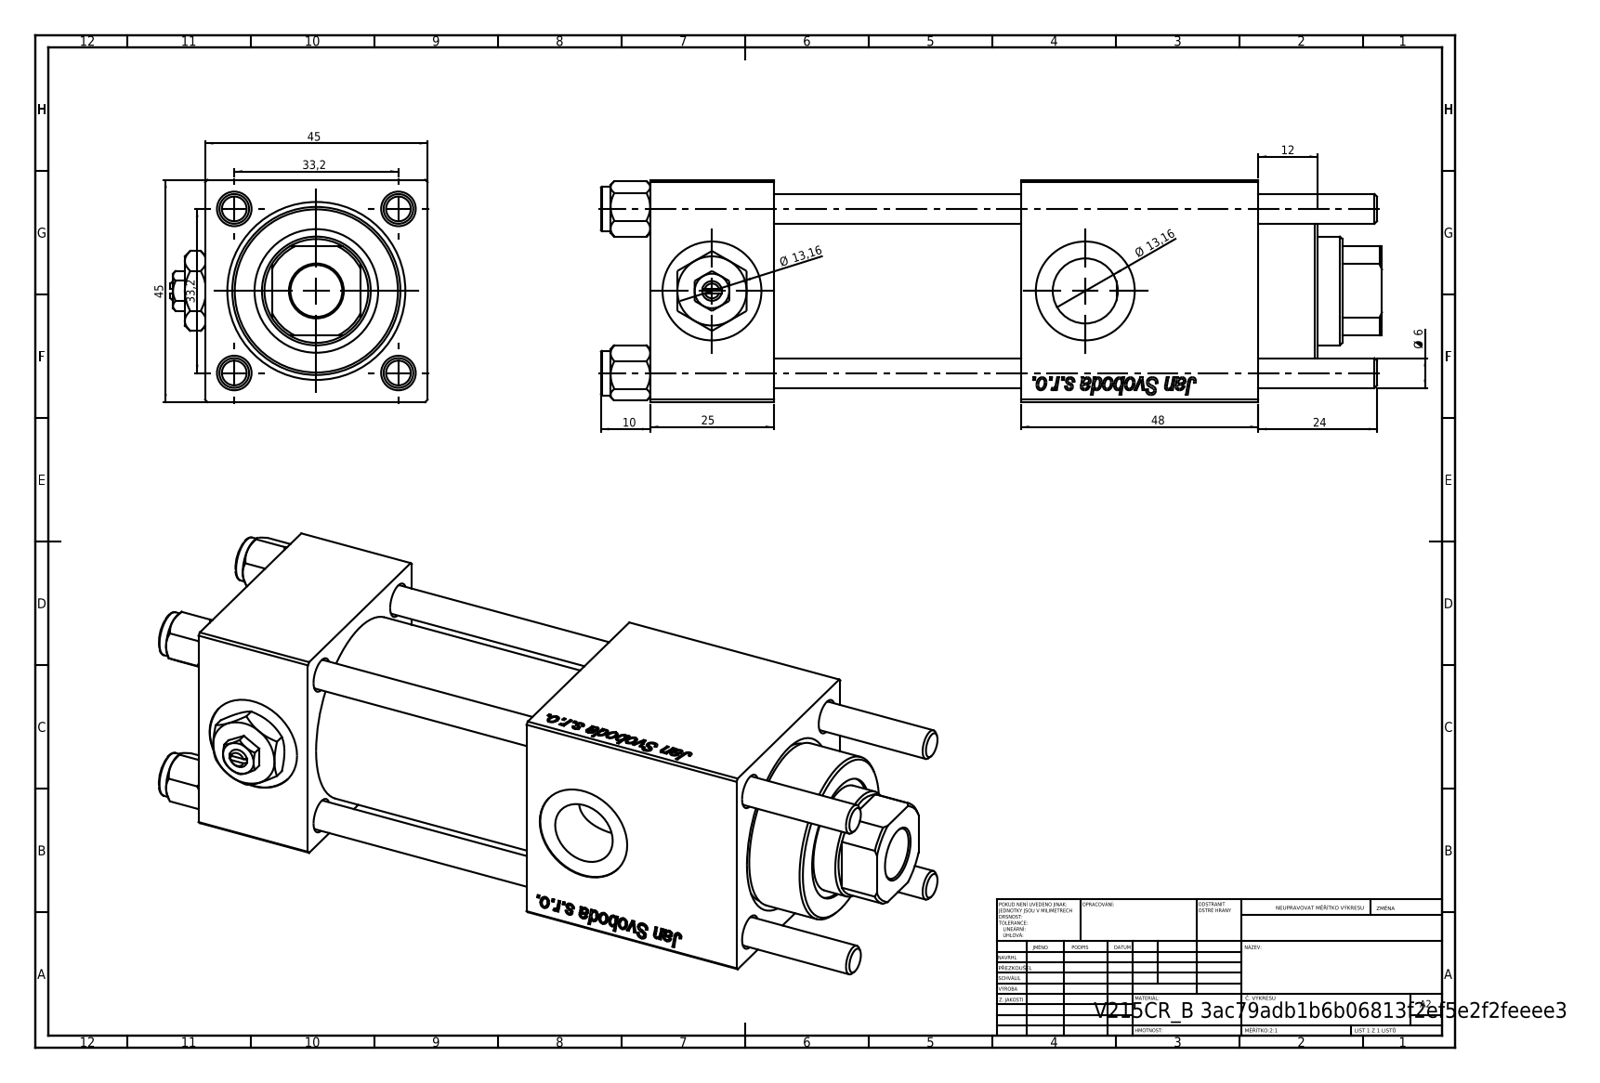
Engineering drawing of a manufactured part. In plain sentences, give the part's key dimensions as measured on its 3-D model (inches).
The part is named "V215CR_B_TYCINKA; Zatka_pro_OIL_PORT; V215CR_B-1; V215_VC_A (+2 more)". Its 3-D file was written by "SolidWorks 2019 (CONFIG_CONTROL_DESIGN)". It is 12 solids with 1208 faces: 454 planar, 84 cylindrical and 670 other. Overall it measures 6.22 by 2.047 by 1.772 inches. Its volume is 13.03 cubic inches and its surface area 120.7 square inches. Round holes: 4 of diameter 0.236, 2 of diameter 0.276, 2 of diameter 0.518, 2 of diameter 0.787, 1 of diameter 0.413, 1 of diameter 0.866, 1 of diameter 0.945, 1 of diameter 0.984, 1 of diameter 1.26, 1 of diameter 1.299. Round bosses or shafts: 4 of diameter 0.354, 1 of diameter 1.496, 1 of diameter 1.339. Partial cylindrical surfaces (rounded edges, fillets, slot ends): 1 of radius 0.413. The main face-to-face distances are 1.772, 0.984, 1.969, 4.843, 2.953, 3.858, 1.89, 3.713, 2.728, 0.76. The hole center spacings are 0.924, 1.307, 1.848, 2.972.
